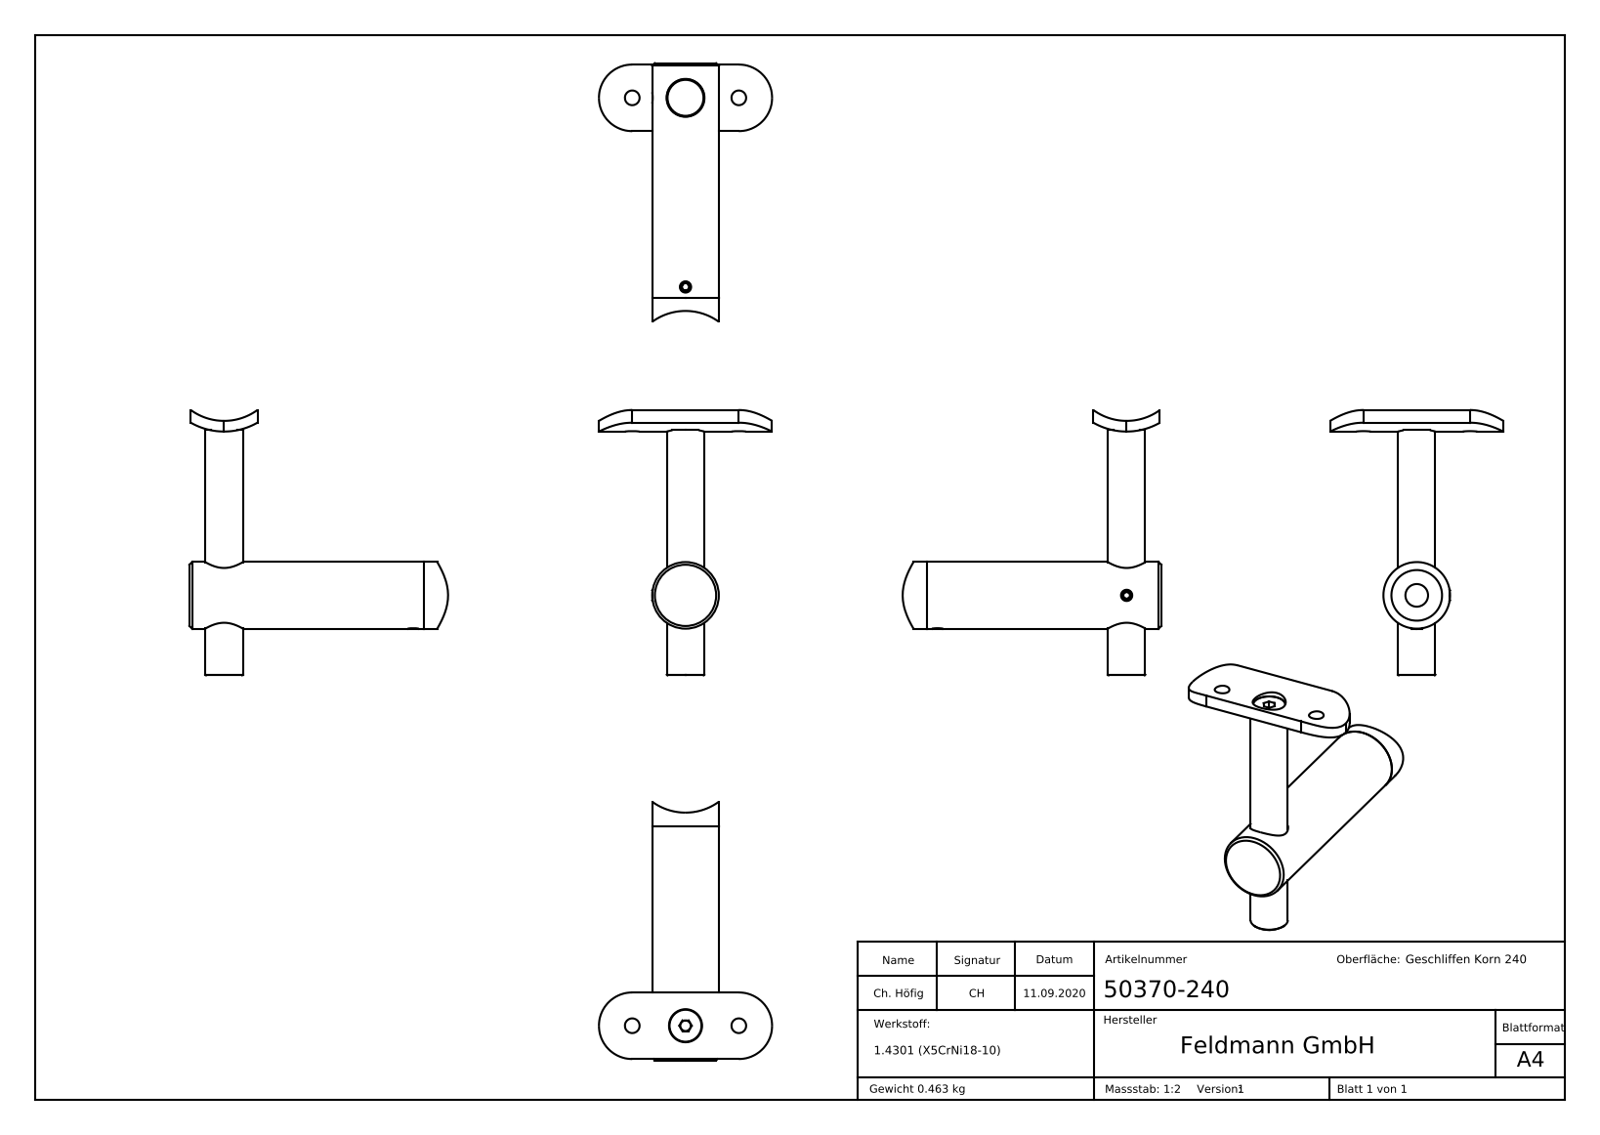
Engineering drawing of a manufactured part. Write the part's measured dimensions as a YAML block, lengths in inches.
part_name: "DIN914_DIN 914 M5x5; DIN913; 5037X-240 Teil1; 50370-240 (+8 more)"
step_written_by: "SolidWorks 2018 (CONFIG_CONTROL_DESIGN)"
units: inches
bodies: {solids: 7, faces: 353, planar: 139, cylindrical: 75, other: 139}
overall_size: [3.92, 3.822, 3.465]
volume: 3.58
surface_area: 33.78
round_holes:
  - {diameter: 0.165, count: 2}
  - {diameter: 0.217, count: 2}
  - {diameter: 0.197, count: 1}
  - {diameter: 0.315, count: 1}
  - {diameter: 0.335, count: 1}
  - {diameter: 0.488, count: 1}
  - {diameter: 0.551, count: 1}
  - {diameter: 0.559, count: 1}
  - {diameter: 0.63, count: 1}
  - {diameter: 0.748, count: 1}
round_bosses_or_shafts:
  - {diameter: 0.197, count: 2}
  - {diameter: 0.984, count: 1}
  - {diameter: 0.472, count: 1}
  - {diameter: 0.236, count: 1}
partial_cylinders:
  - {radius: 0.492, count: 2}
  - {radius: 0.835, count: 2}
  - {radius: 0.319, count: 1}
  - {radius: 0.992, count: 1}
face_to_face_distances: [3.465, 0.118, 3.583, 3.563, 3.445, 0.02, 2.579, 2.461, 0.984, 1.004]
hole_center_spacings: [0.787, 2.904, 1.575, 2.795]
